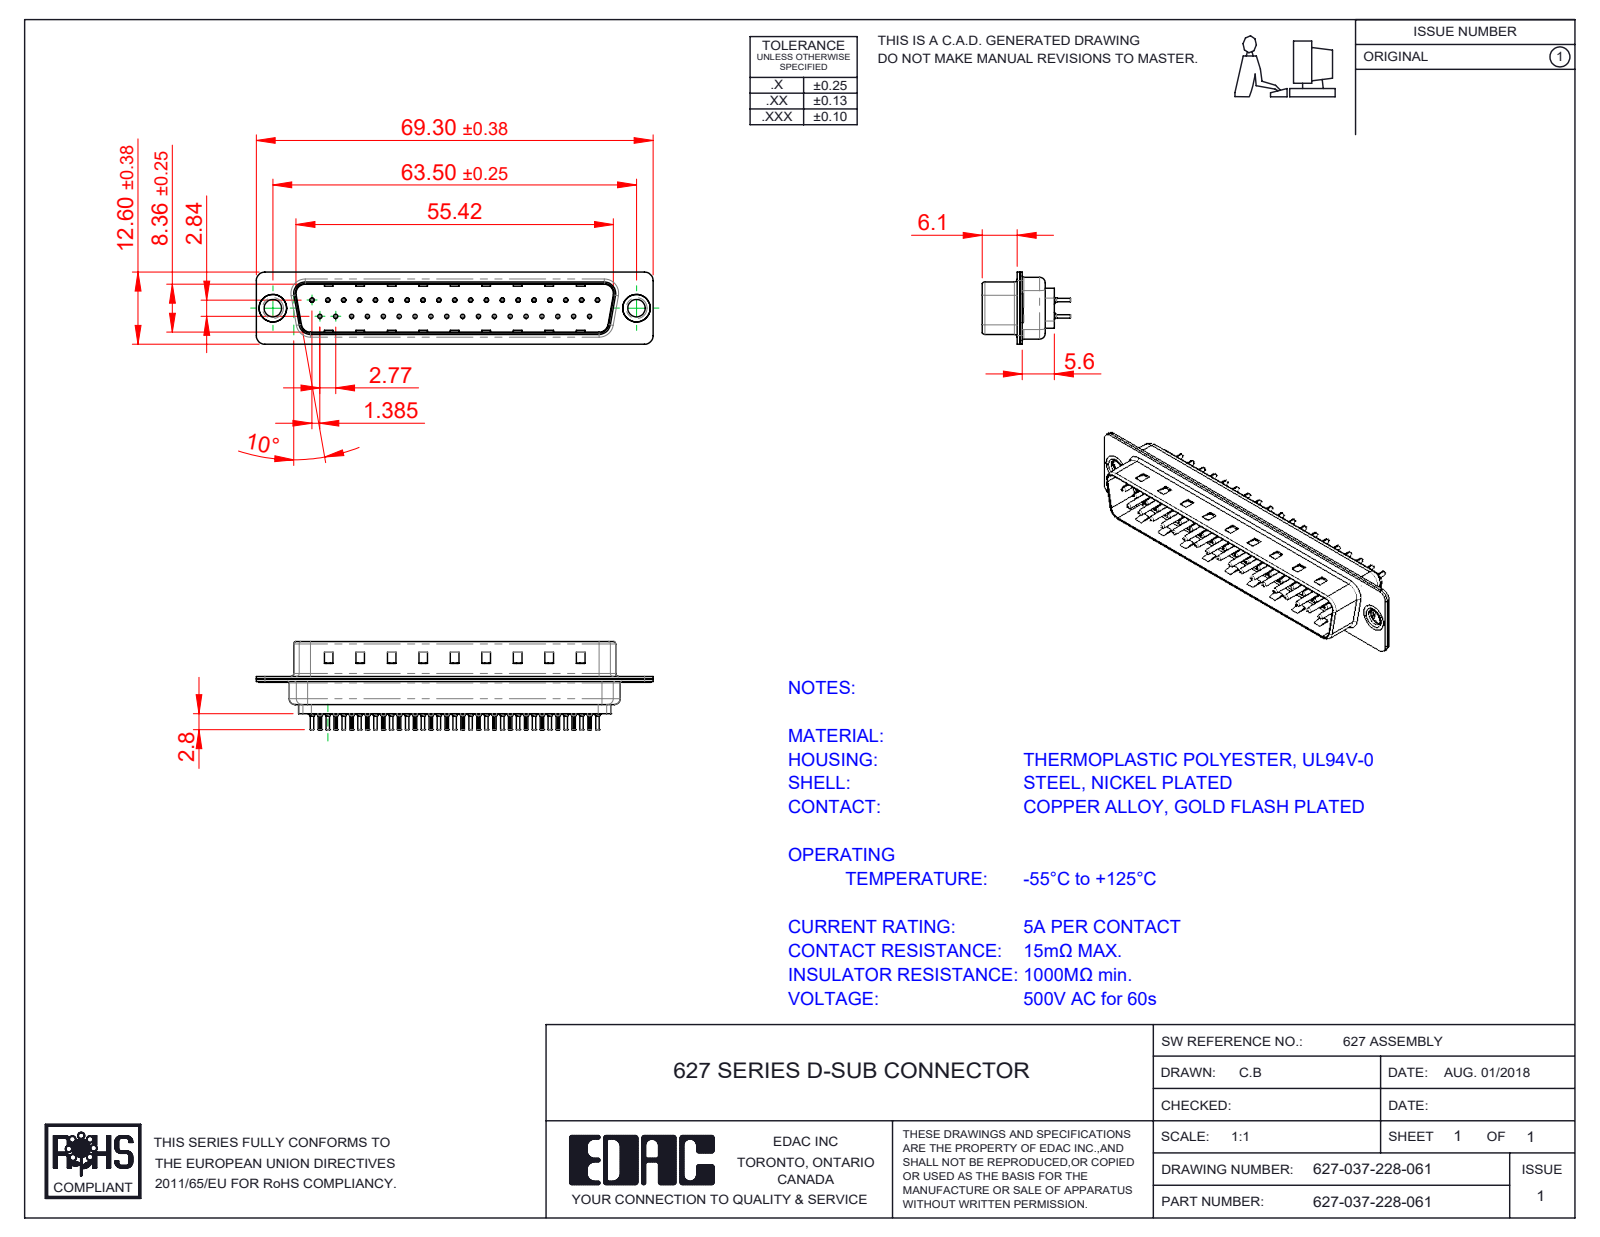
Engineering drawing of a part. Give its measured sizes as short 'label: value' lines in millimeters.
name: 627 Thru Hole Rivet; 627 Shell Rear_37 Contacts; 627-037-228-061; 627 Housing_37 FF (+3 more)
written by: SolidWorks 2020 (CONFIG_CONTROL_DESIGN)
unit: mm
bodies: 43 solids, 4097 faces (1097 planar, 1573 cylindrical, 1427 other)
size: 69.3 × 18.8 × 12.6
volume: 4 478 mm³; area: 12 151 mm²
holes: 37× ⌀0.2, 37× ⌀0.35, 37× ⌀1.1, 37× ⌀1.6, 2× ⌀3.05, 2× ⌀4, 2× ⌀4.8
bosses: 37× ⌀2, 37× ⌀1.5, 37× ⌀0.75, 37× ⌀0.6, 2× ⌀5, 2× ⌀4.9, 2× ⌀3.55
rounds: 74× R0.1, 16× R1.5, 12× R2, 8× R0.5, 8× R1.6, 4× R0.25, 4× R0.6, 4× R0.65
face distances: 0.4, 6.05, 0.82, 9.58, 0.45, 8.4, 0.68, 7.68, 1.5, 1.08
hole spacings: 3.16, 2.77, 5.54, 8.31, 5.04, 10.1, 11.08, 12.78
